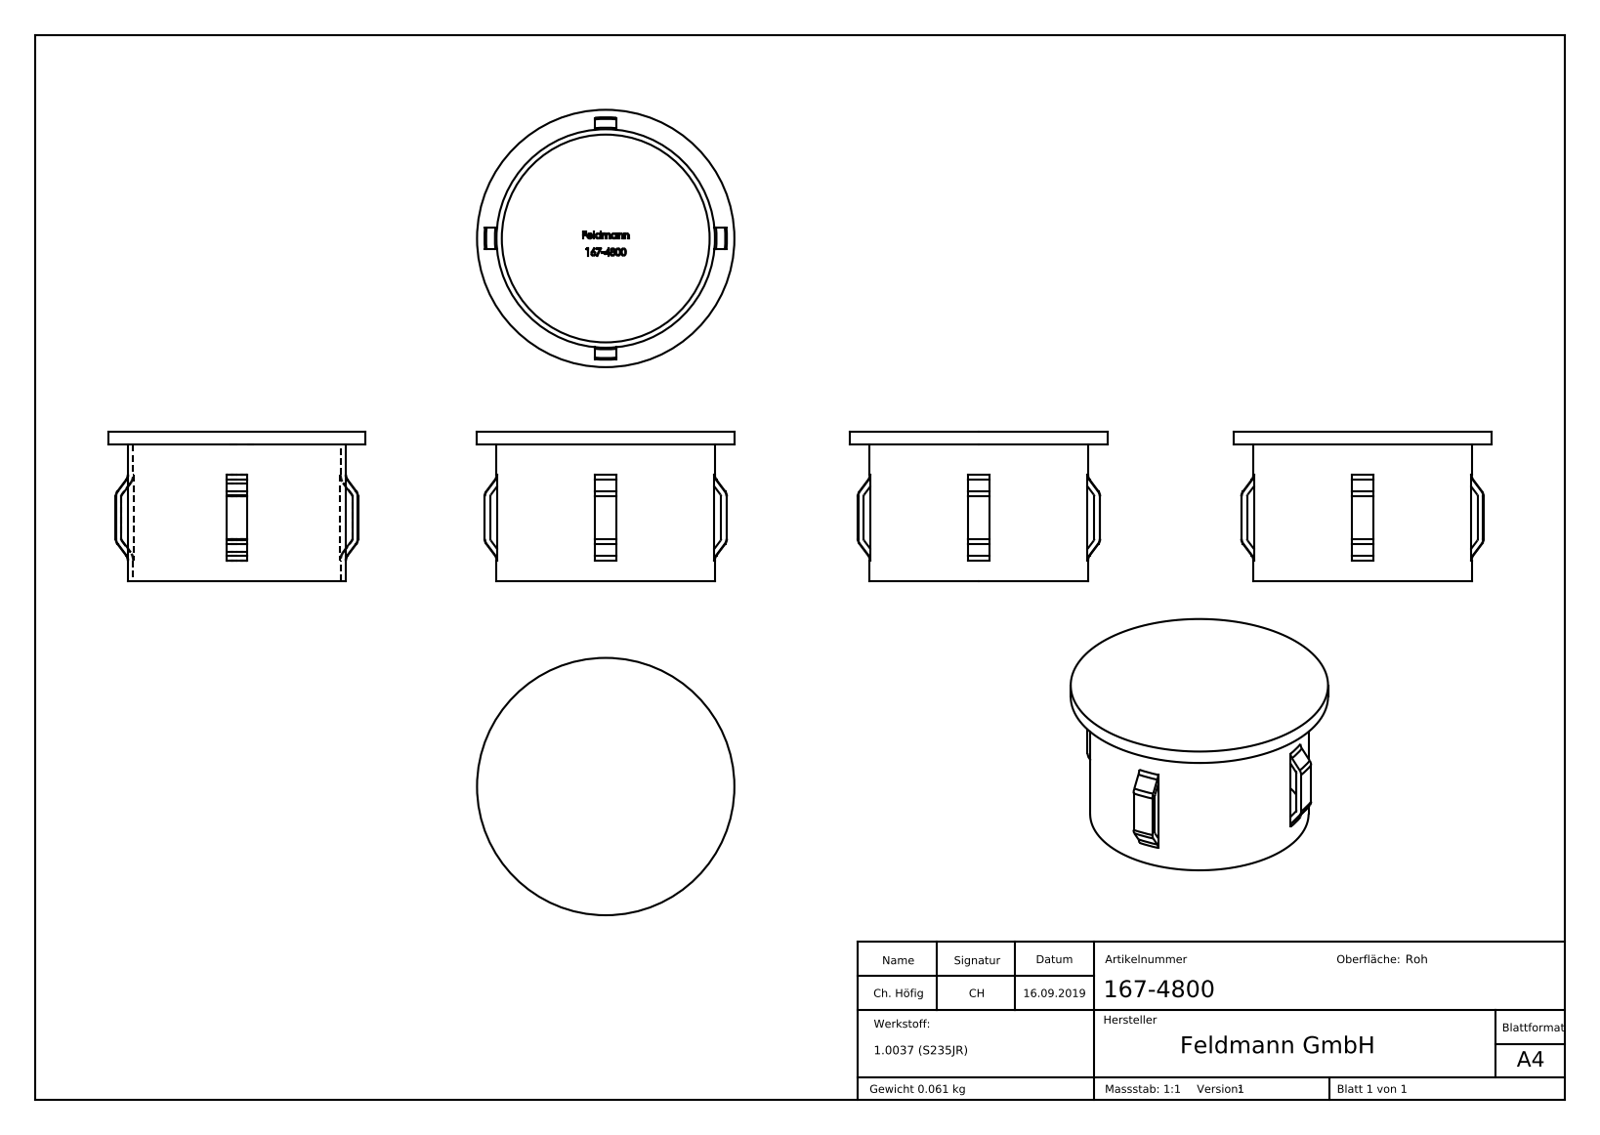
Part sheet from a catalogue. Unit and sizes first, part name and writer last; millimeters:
Units: millimetres
Overall size (bounding box): 48.3 × 48.3 × 28.2
Round holes (diameter × count): ⌀39 ×1
Round bosses / shafts (diameter × count): ⌀48.3 ×1, ⌀41 ×1
Partial cylindrical surfaces — rounded edges, fillets, slot ends (radius × count): R21.75 ×1, R22.75 ×1
Main face-to-face distances: 2.5, 25.7, 28.2, 4, 2.4, 25.8, 3.88, 2, 2.97, 2.85
Volume: 7 831 mm³ · Surface area: 10 777 mm²
Bodies: 1 solid, 299 faces (131 planar, 16 cylindrical, 152 other)
Part name (STEP PRODUCT): 167-4800
STEP written by: SolidWorks 2015 (CONFIG_CONTROL_DESIGN)
